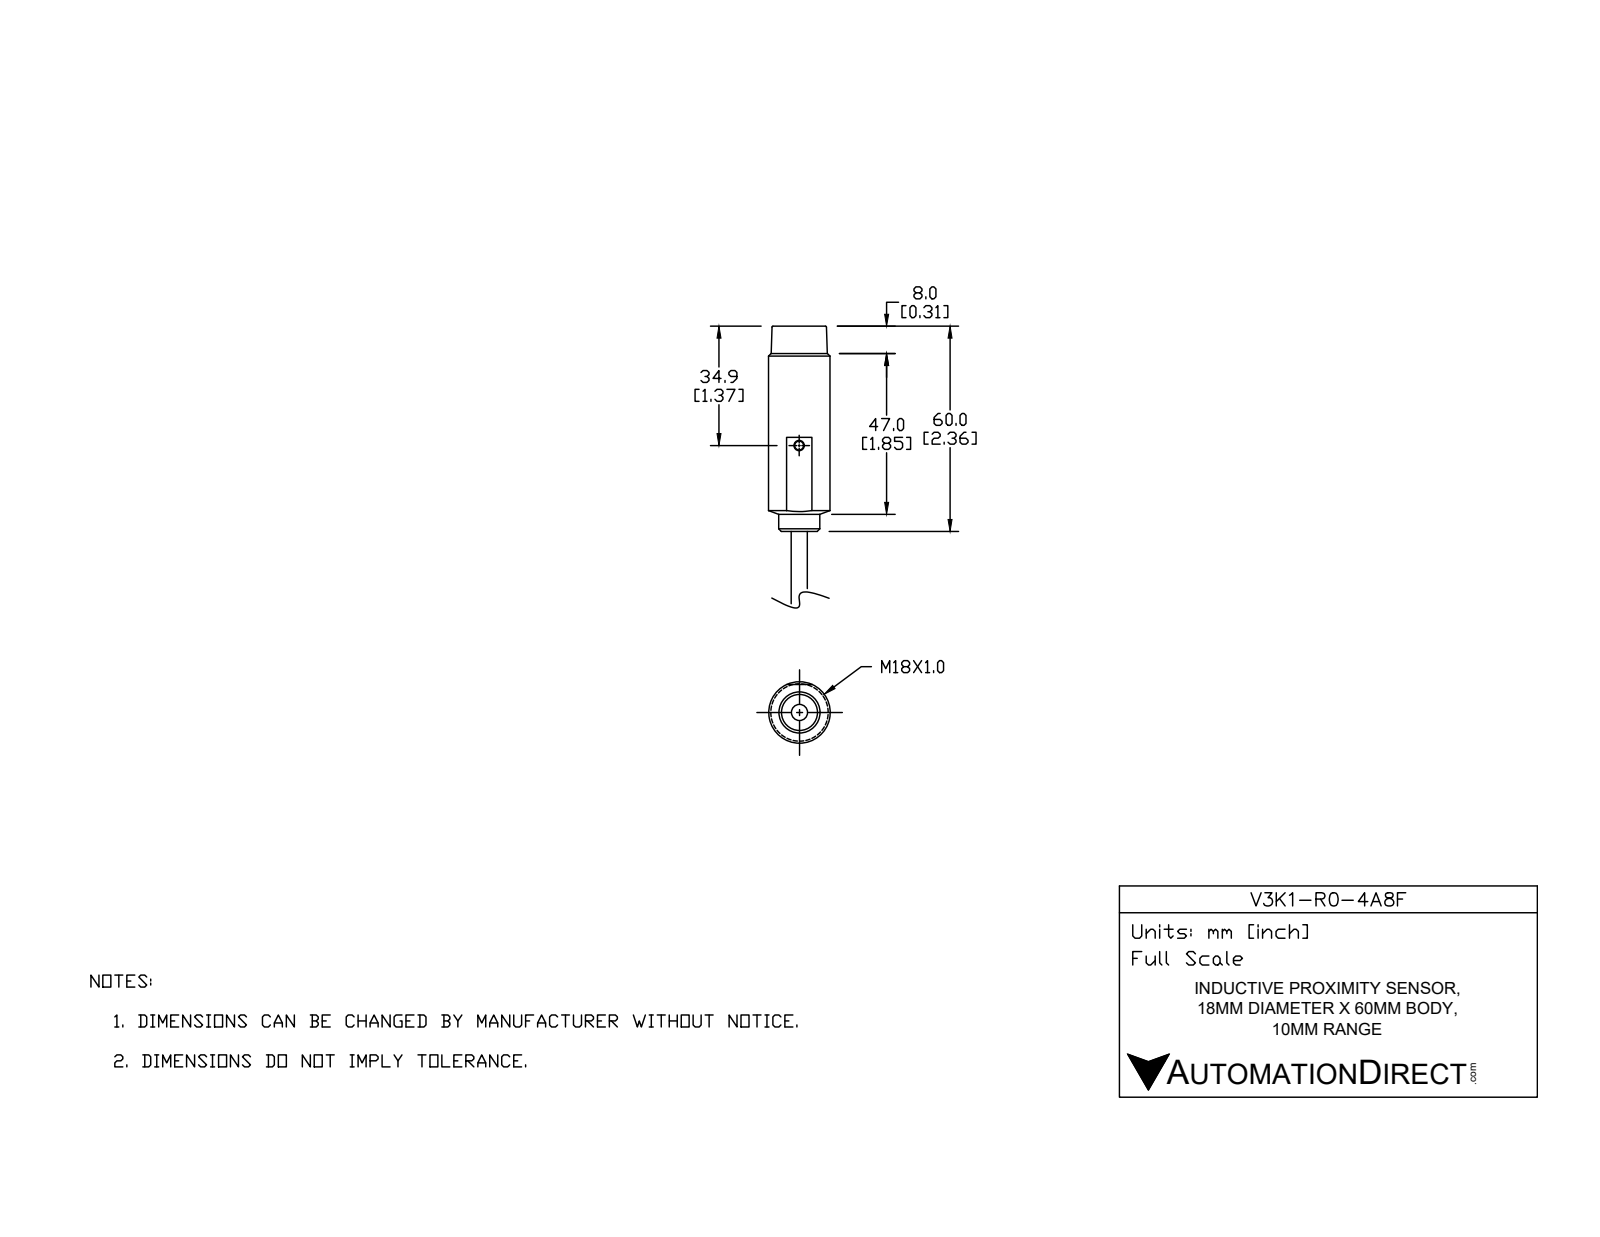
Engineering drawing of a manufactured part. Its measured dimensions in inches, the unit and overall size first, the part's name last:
Units: inches
Overall size (bounding box): 3.937 × 0.709 × 0.709
Round holes (diameter × count): ⌀0.102 ×1
Round bosses / shafts (diameter × count): ⌀0.709 ×1, ⌀0.472 ×1, ⌀0.185 ×1
Main face-to-face distances: 2.362, 3.937, 1.575, 0.047, 1.28, 1.083, 2.657, 0.315, 0.965, 2.047
Volume: 0.894 in³ · Surface area: 6.577 in²
Bodies: 1 solid, 17 faces (7 planar, 4 cylindrical, 6 other)
Part name (STEP PRODUCT): V3K1_4A_fig
STEP written by: ST-DEVELOPER v16.7 (AUTOMOTIVE_DESIGN)
